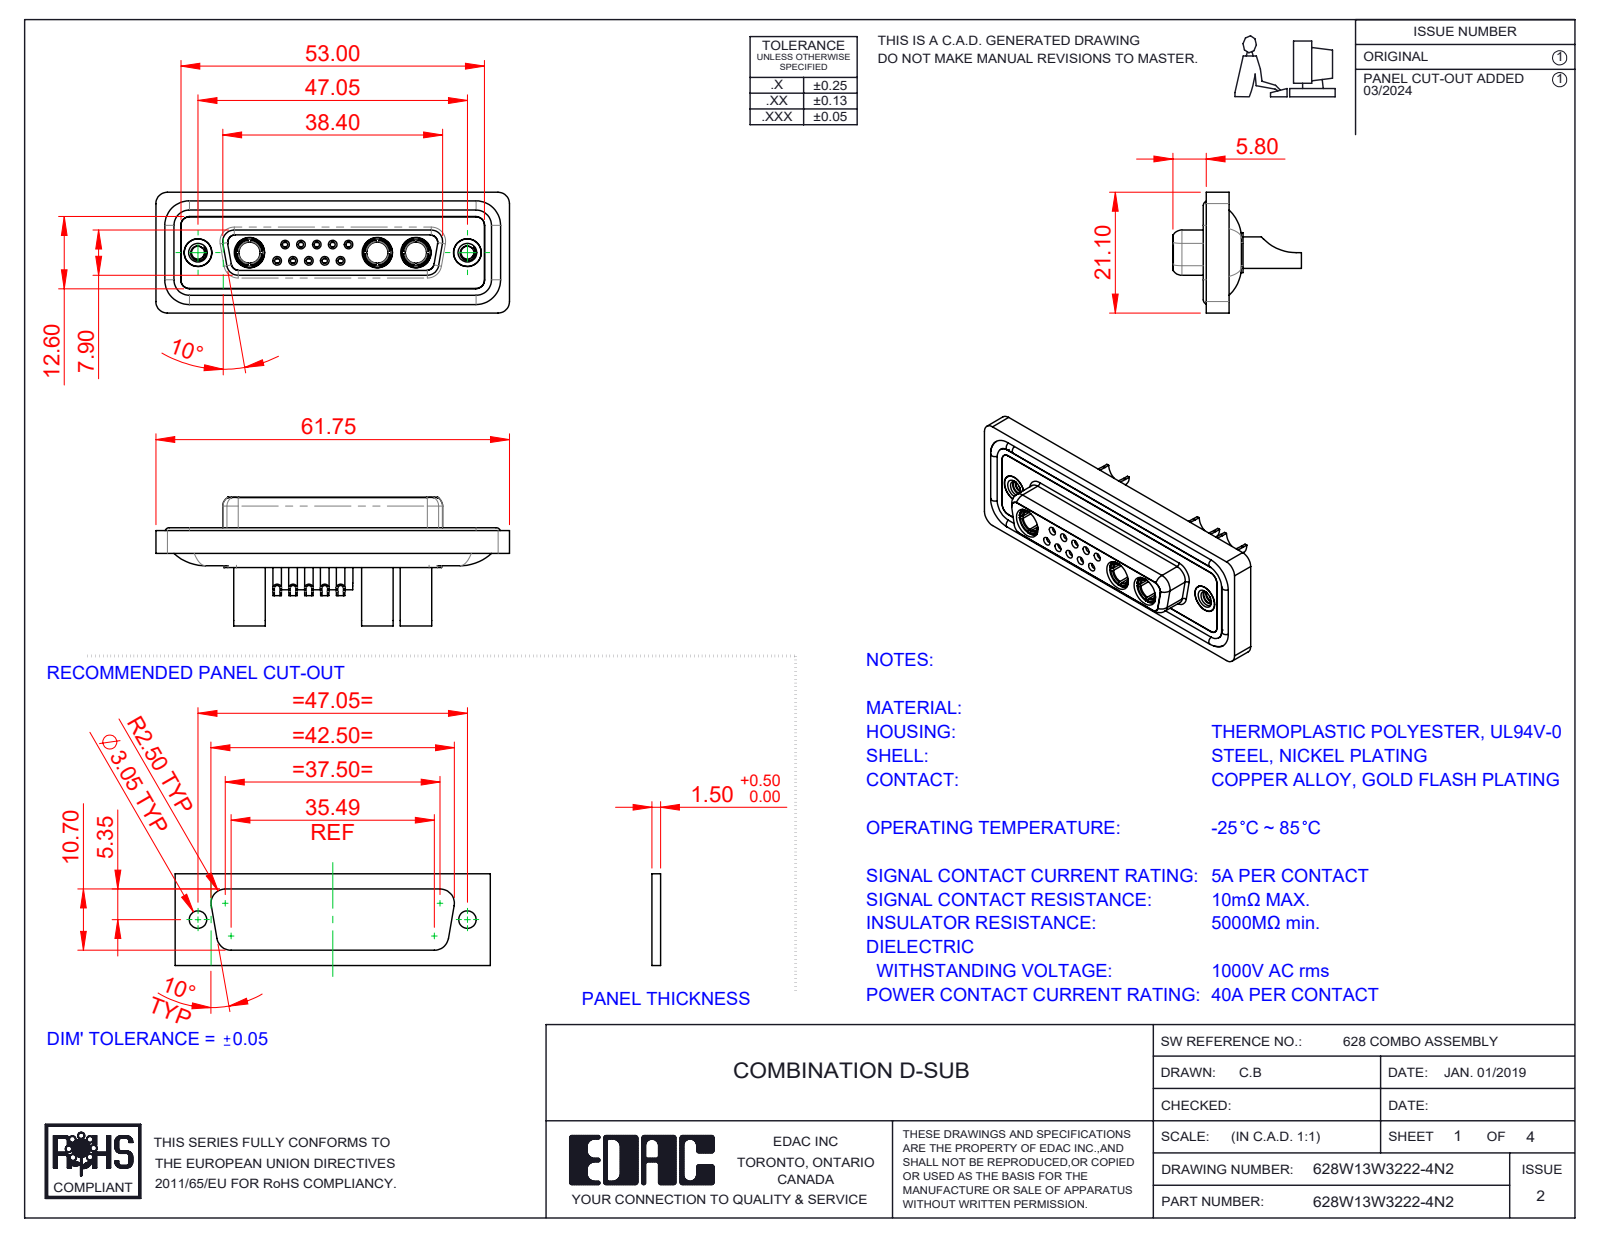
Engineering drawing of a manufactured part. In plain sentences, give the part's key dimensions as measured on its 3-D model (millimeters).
The part is named "628Combo Shell Rear_25 Contacts; 628Combo Contact Row 2_22; 628Combo Shell Front_25 Contacts; 628Combo Contact Row 1_22 (+5 more)". Its 3-D file was written by "SolidWorks 2023 (CONFIG_CONTROL_DESIGN)". It is 23 solids with 1167 faces: 368 planar, 470 cylindrical and 329 other. Overall it measures 61.75 by 22.45 by 21.1 millimeters. Its volume is 8 413 cubic millimeters and its surface area 14 233 square millimeters. Round holes: 10 of diameter 0.9, 10 of diameter 1, 10 of diameter 1.1, 10 of diameter 1.5, 10 of diameter 2, 5 of diameter 1.6, 5 of diameter 1.7, 5 of diameter 4.85, 3 of diameter 3.7, 3 of diameter 4.6, 3 of diameter 5.3, 2 of diameter 2.26. Round bosses or shafts: 10 of diameter 2.2, 9 of diameter 1.6, 3 of diameter 5.5, 3 of diameter 5.2, 3 of diameter 4.96, 3 of diameter 4.75, 3 of diameter 3.75, 2 of diameter 4.95. Partial cylindrical surfaces (rounded edges, fillets, slot ends): 22 of radius 1.5, 18 of radius 2, 8 of radius 1.35, 8 of radius 1.6, 6 of radius 1, 4 of radius 0.25, 4 of radius 0.5, 4 of radius 0.6. The main face-to-face distances are 0.4, 7.45, 1.8, 5.65, 0.5, 6.6, 7.05, 1.6, 2.9, 1.1. The hole center spacings are 3.16, 2.77, 5.03, 5.04, 5.54, 8.31, 7.49, 2.76.
